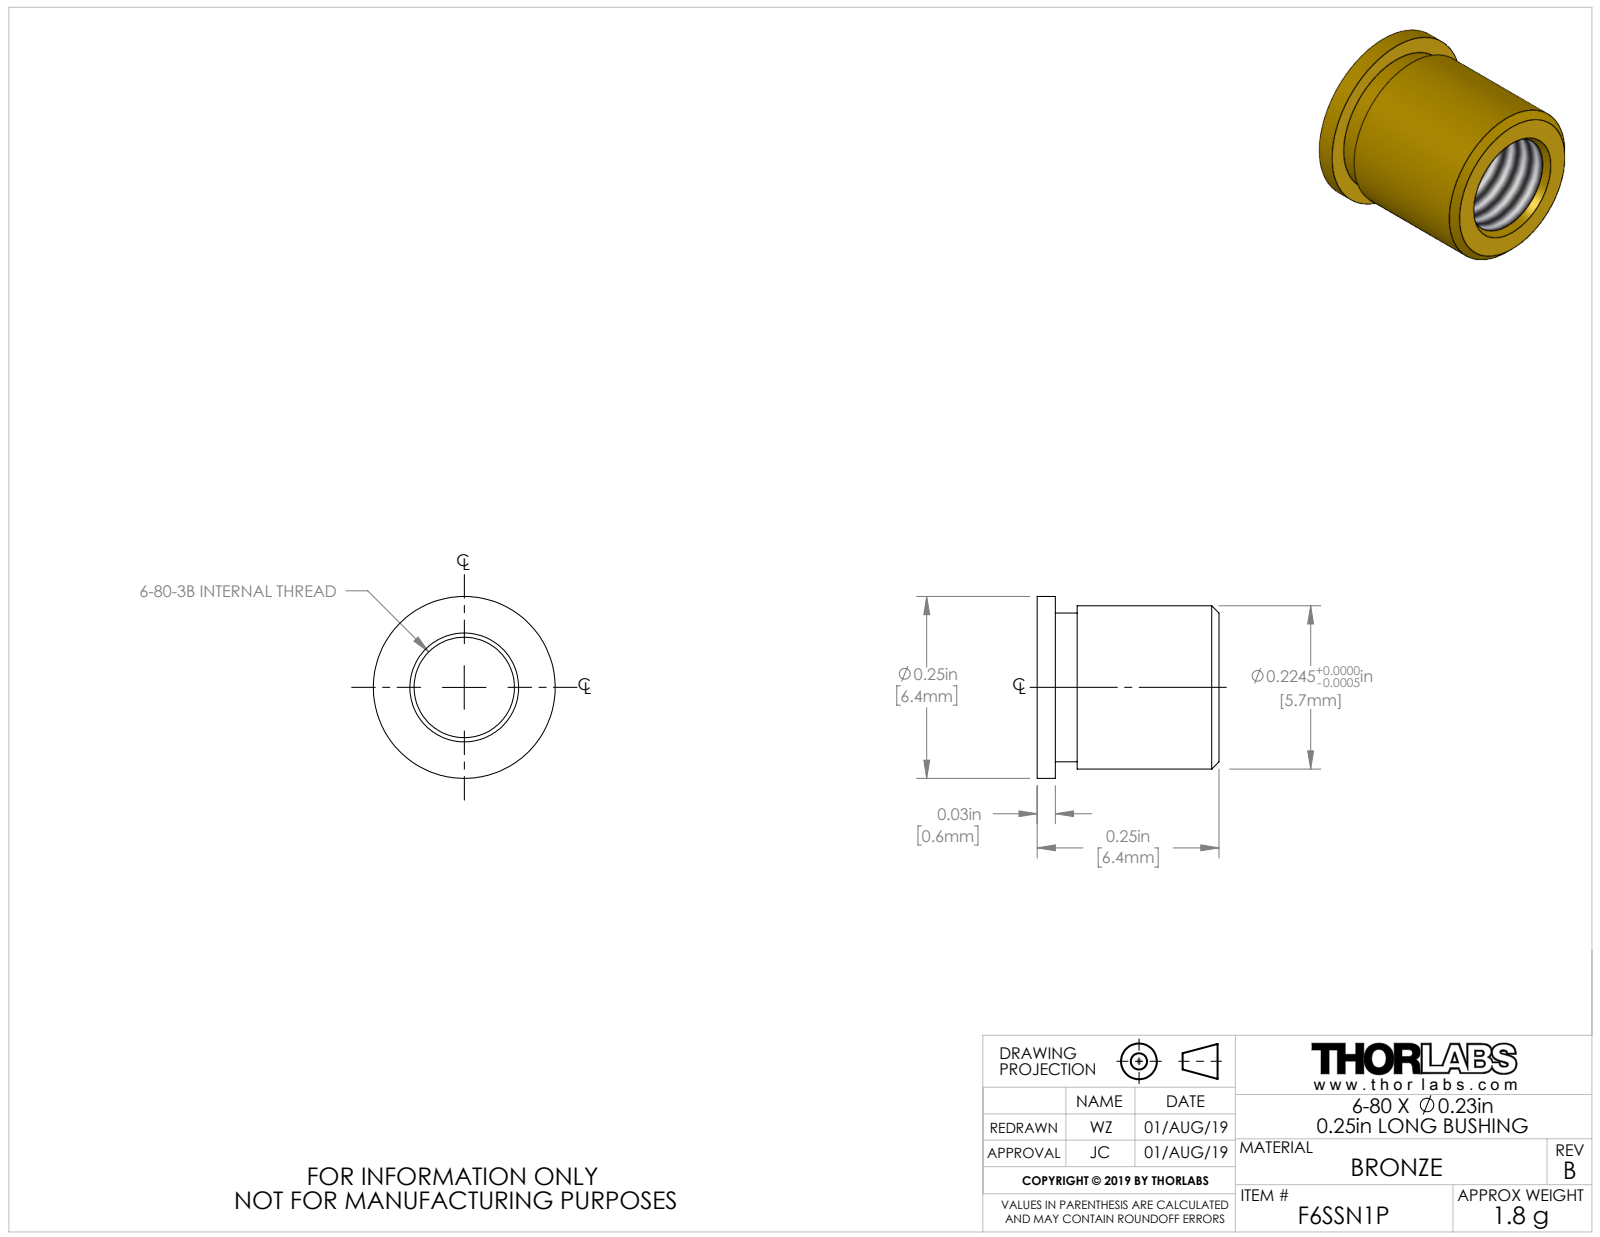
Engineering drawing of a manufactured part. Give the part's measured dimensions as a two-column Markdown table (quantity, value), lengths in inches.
| quantity | value |
| --- | --- |
| part name | 18998-E0W |
| STEP written by | SolidWorks 2007 (AUTOMOTIVE_DESIGN) |
| units | inches |
| bodies | 1 solid, 18 faces (4 planar, 8 cylindrical, 6 other) |
| overall size | 0.25 × 0.25 × 0.25 |
| volume | 0.006 in³ |
| surface area | 0.36 in² |
| round holes (diameter × count) | 0.138 × 1 |
| round bosses / shafts (diameter × count) | 0.25 × 1, 0.224 × 1, 0.204 × 1 |
| main face-to-face distances | 0.025, 0.25, 0.225, 0.055, 0.03, 0.195 |
